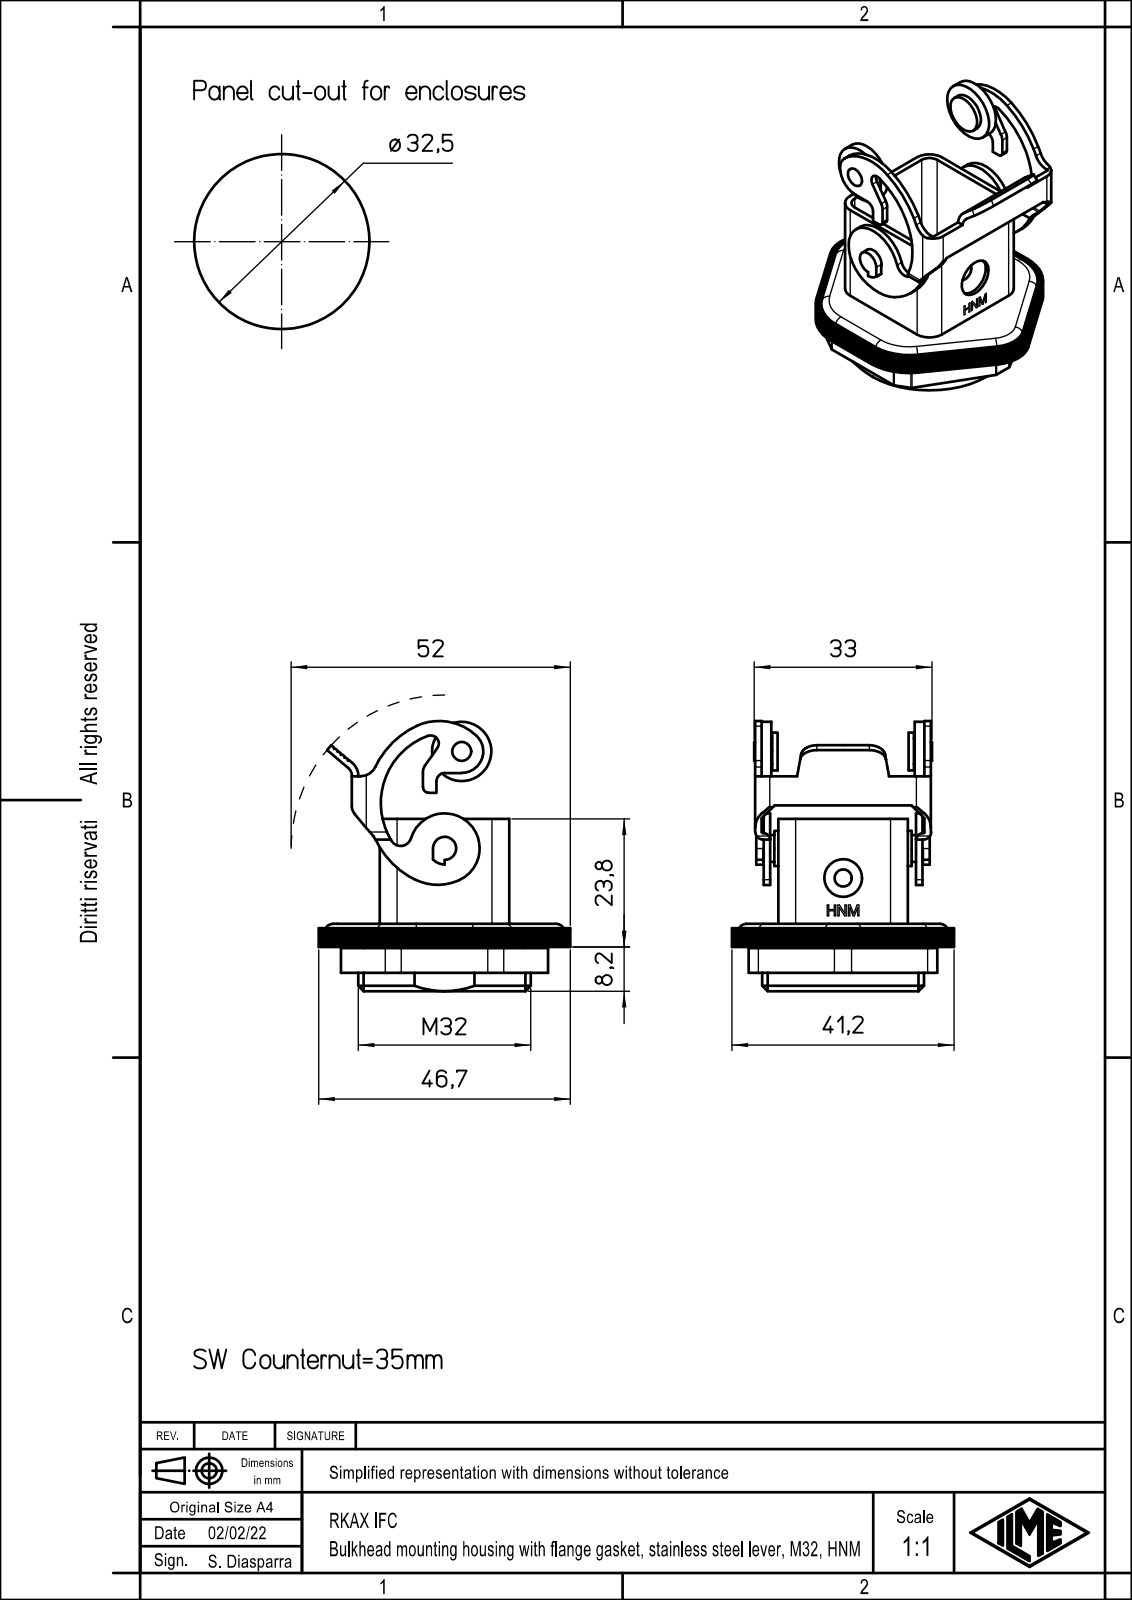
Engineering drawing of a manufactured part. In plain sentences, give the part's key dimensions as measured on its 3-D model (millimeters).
The part is named "RKAX_IFC". Its 3-D file was written by "Creo Elements/Direct Modeling 20.1B 02-Apr-2019 (C) Parametric Technology GmbH (AUTOMOTIVE_DESIGN)". It is 1 solid with 301 faces: 153 planar, 137 cylindrical and 11 other. Overall it measures 50.16 by 46.67 by 41.2 millimeters. Its volume is 11 556 cubic millimeters and its surface area 11 665 square millimeters. Round holes: 1 of diameter 3.2, 1 of diameter 7, 1 of diameter 33. Round bosses or shafts: 1 of diameter 29.8, 1 of diameter 11, 1 of diameter 7, 1 of diameter 6.5, 1 of diameter 5, 1 of diameter 4.8, 1 of diameter 4.3, 1 of diameter 3.5. Partial cylindrical surfaces (rounded edges, fillets, slot ends): 15 of radius 0.25, 10 of radius 0.4, 8 of radius 1.5, 8 of radius 2, 5 of radius 3, 5 of radius 3.2, 4 of radius 1.4, 4 of radius 10.1. The main face-to-face distances are 1.2, 22.8, 21.6, 24, 4.3, 3.4, 4.5, 28, 5.2, 1.8.
